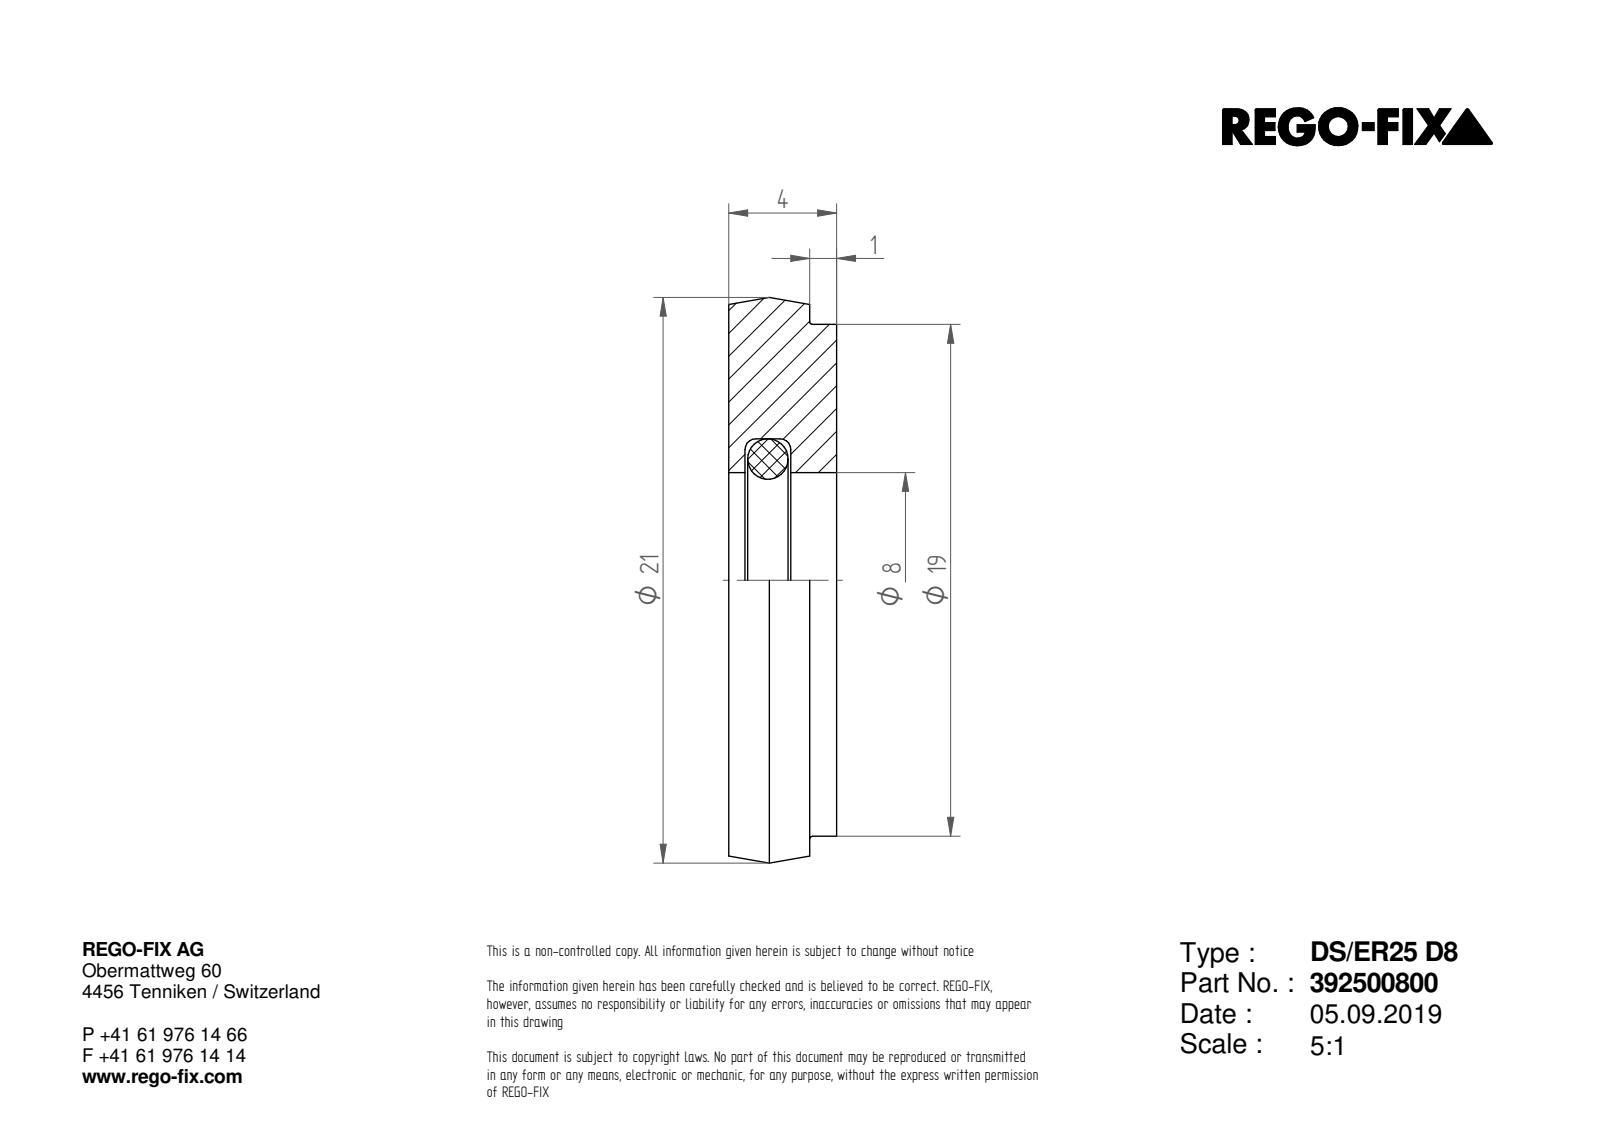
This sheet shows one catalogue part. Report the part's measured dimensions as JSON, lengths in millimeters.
{"part_name": "NOCUT", "step_written_by": "SIEMENS PLM Software Solid Edge ST10 (AUTOMOTIVE_DESIGN)", "units": "millimeters", "bodies": {"solids": 1, "faces": 7, "planar": 3, "cylindrical": 3, "other": 1}, "overall_size": [21, 21, 4], "volume_mm3": 1122, "surface_area_mm2": 948, "round_holes": [[8, 1]], "round_bosses_or_shafts": [[21, 1], [19, 1]], "face_to_face_distances": [4, 1, 3]}
